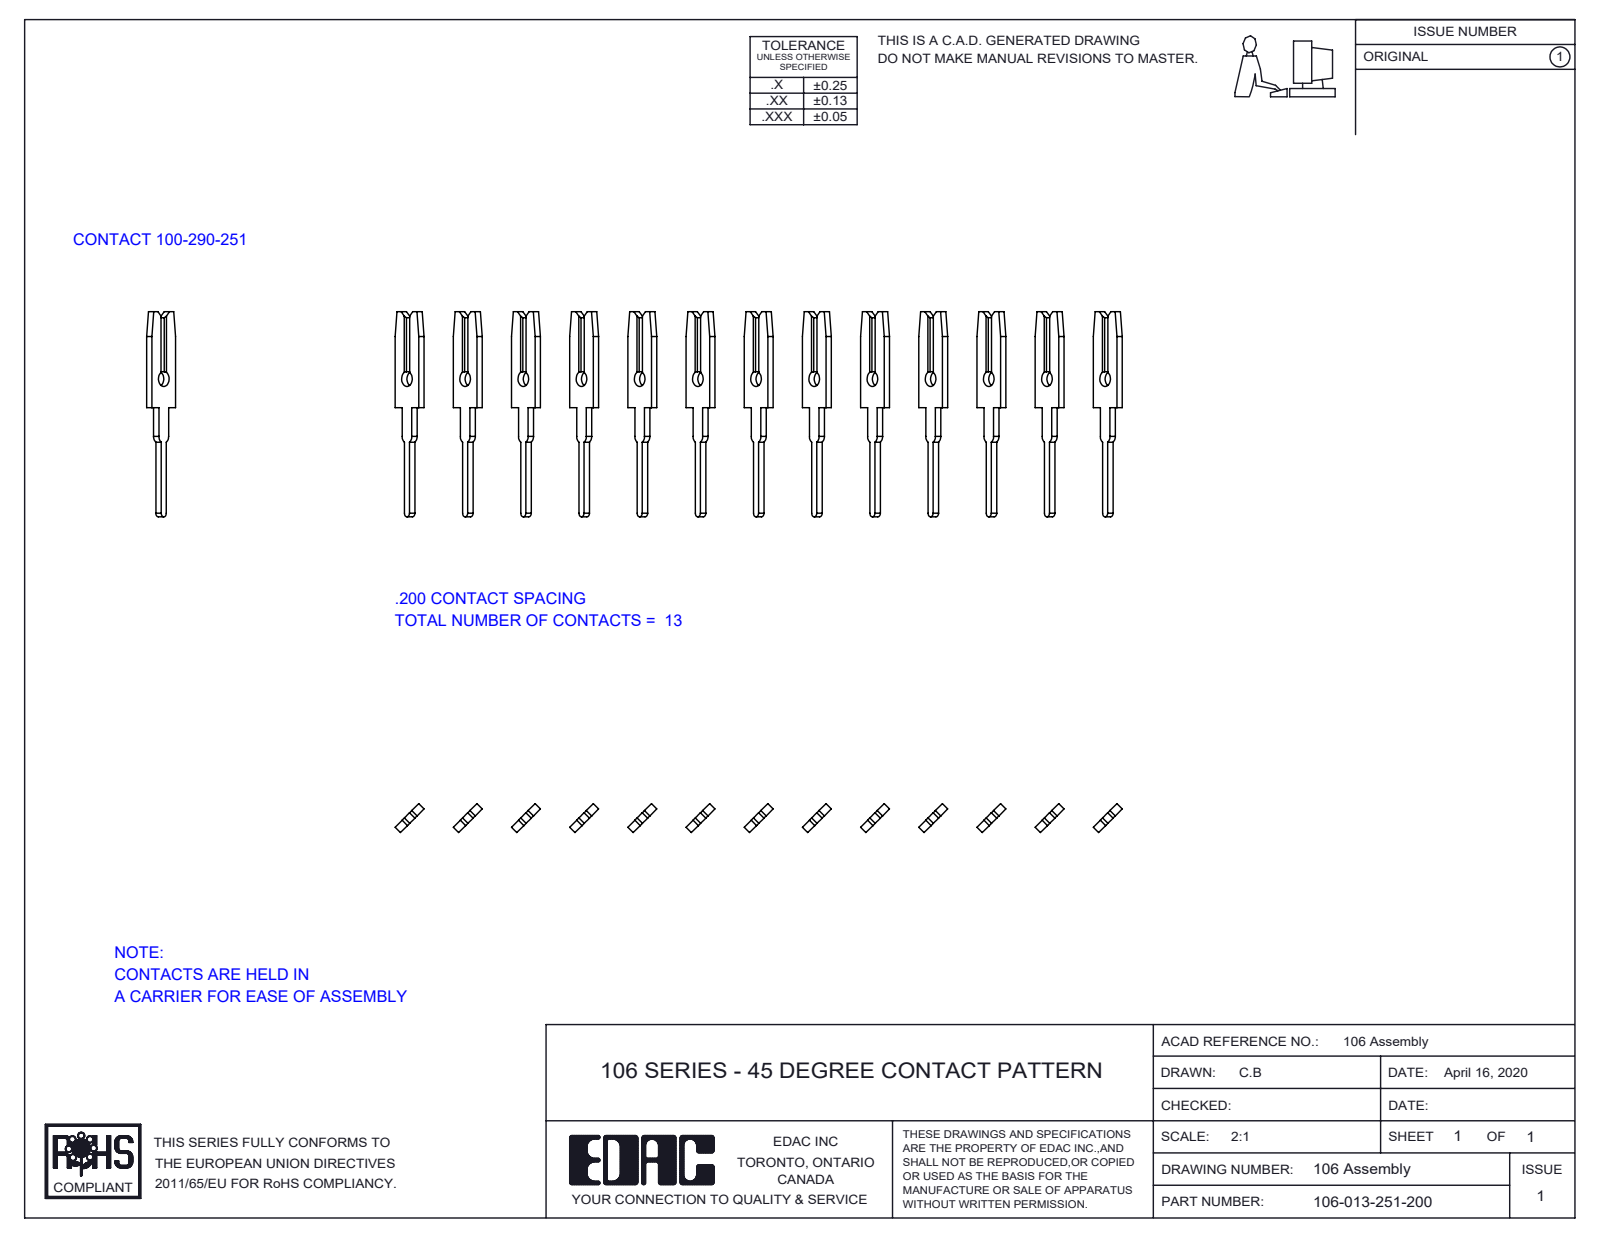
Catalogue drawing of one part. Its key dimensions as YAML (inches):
part_name: "106-013-251-200; 100-290-001_100-290-251"
step_written_by: "SolidWorks 2016 (CONFIG_CONTROL_DESIGN)"
units: inches
bodies: {solids: 13, faces: 364, planar: 286, cylindrical: 78, other: 0}
overall_size: [2.5, 0.705, 0.1]
volume: 0.015
surface_area: 1.811
round_holes:
  - {diameter: 0.052, count: 13}
partial_cylinders:
  - {radius: 0.012, count: 13}
  - {radius: 0.024, count: 13}
face_to_face_distances: [0.141, 0.283, 0.707, 0.848, 0.566, 0.424, 0.424, 0.026, 0.822, 0.283]
hole_center_spacings: [0.141, 0.283, 0.424, 0.566, 0.707, 0.848, 1.131, 0.566]
